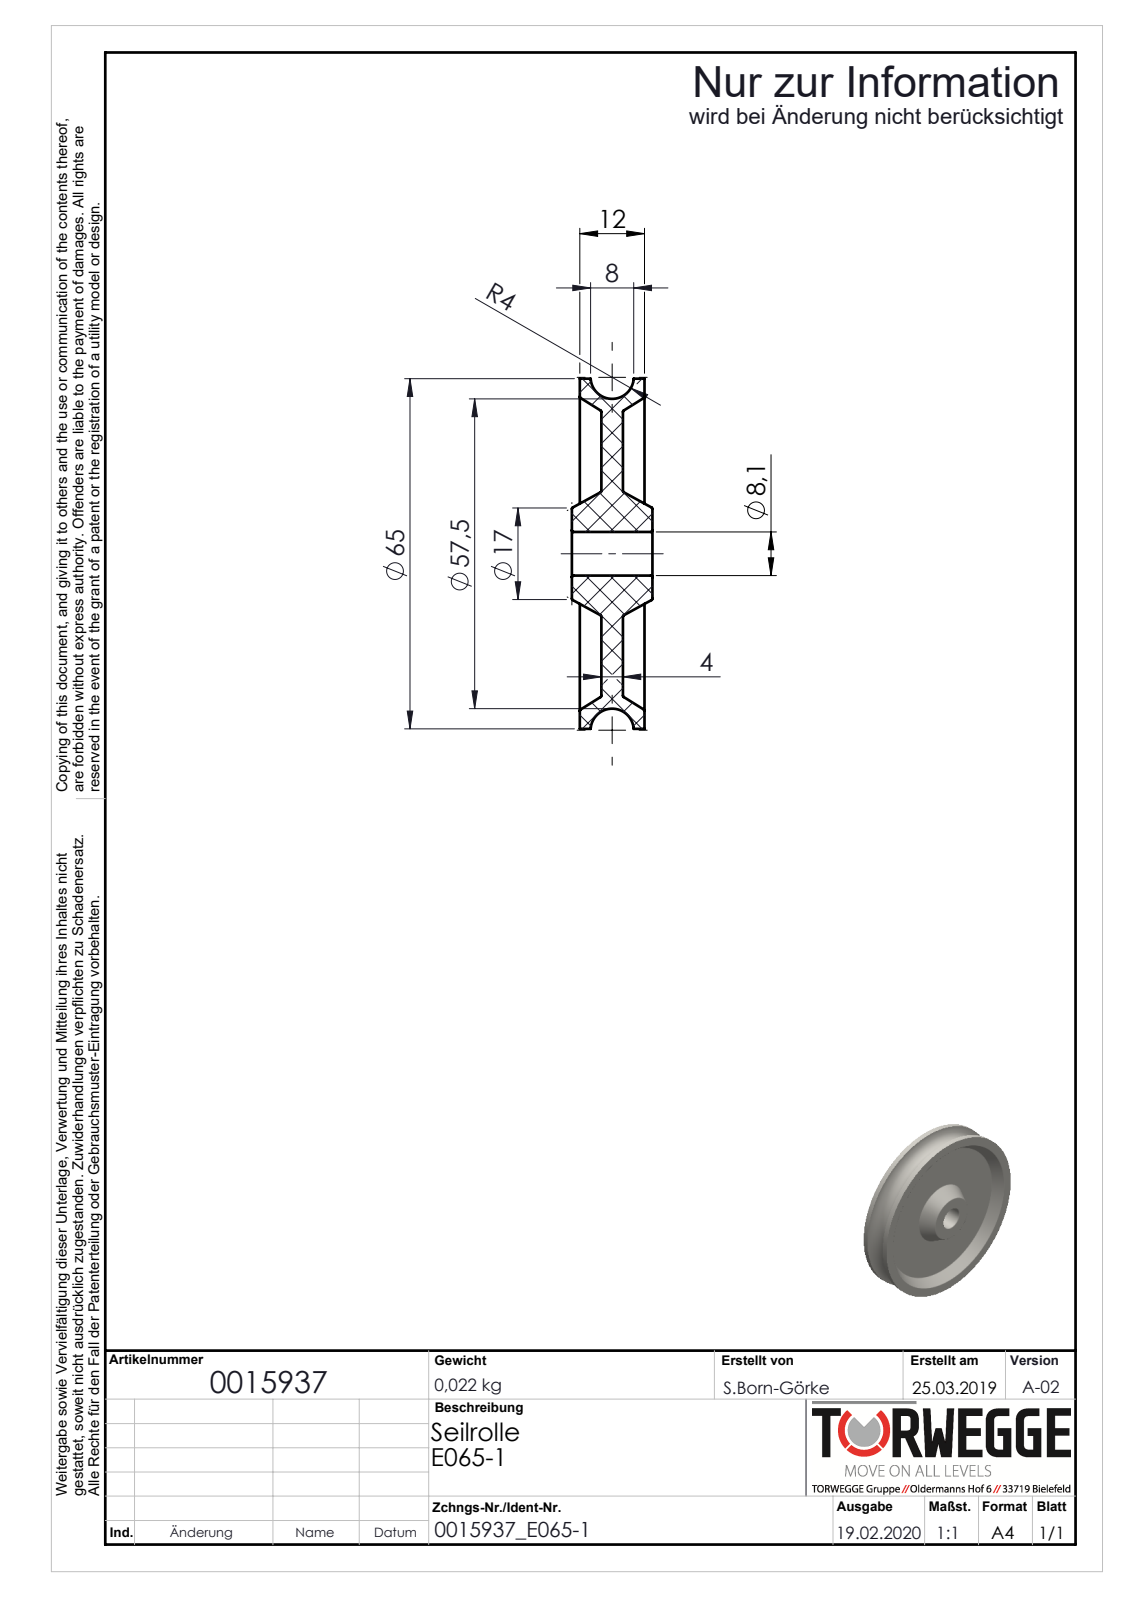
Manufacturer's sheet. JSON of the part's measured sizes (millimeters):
{"part_name": "0015937_E065-1_(A-02)", "step_written_by": "SolidWorks 2018 (AUTOMOTIVE_DESIGN)", "units": "millimeters", "bodies": {"solids": 1, "faces": 48, "planar": 6, "cylindrical": 6, "other": 36}, "overall_size": [65, 65, 14.94], "volume_mm3": 18652, "surface_area_mm2": 11158, "round_holes": [[8.1, 1]], "round_bosses_or_shafts": [[65, 1]], "face_to_face_distances": [4, 8, 12, 1.47, 5.47, 9.47, 13.47, 14.94]}
